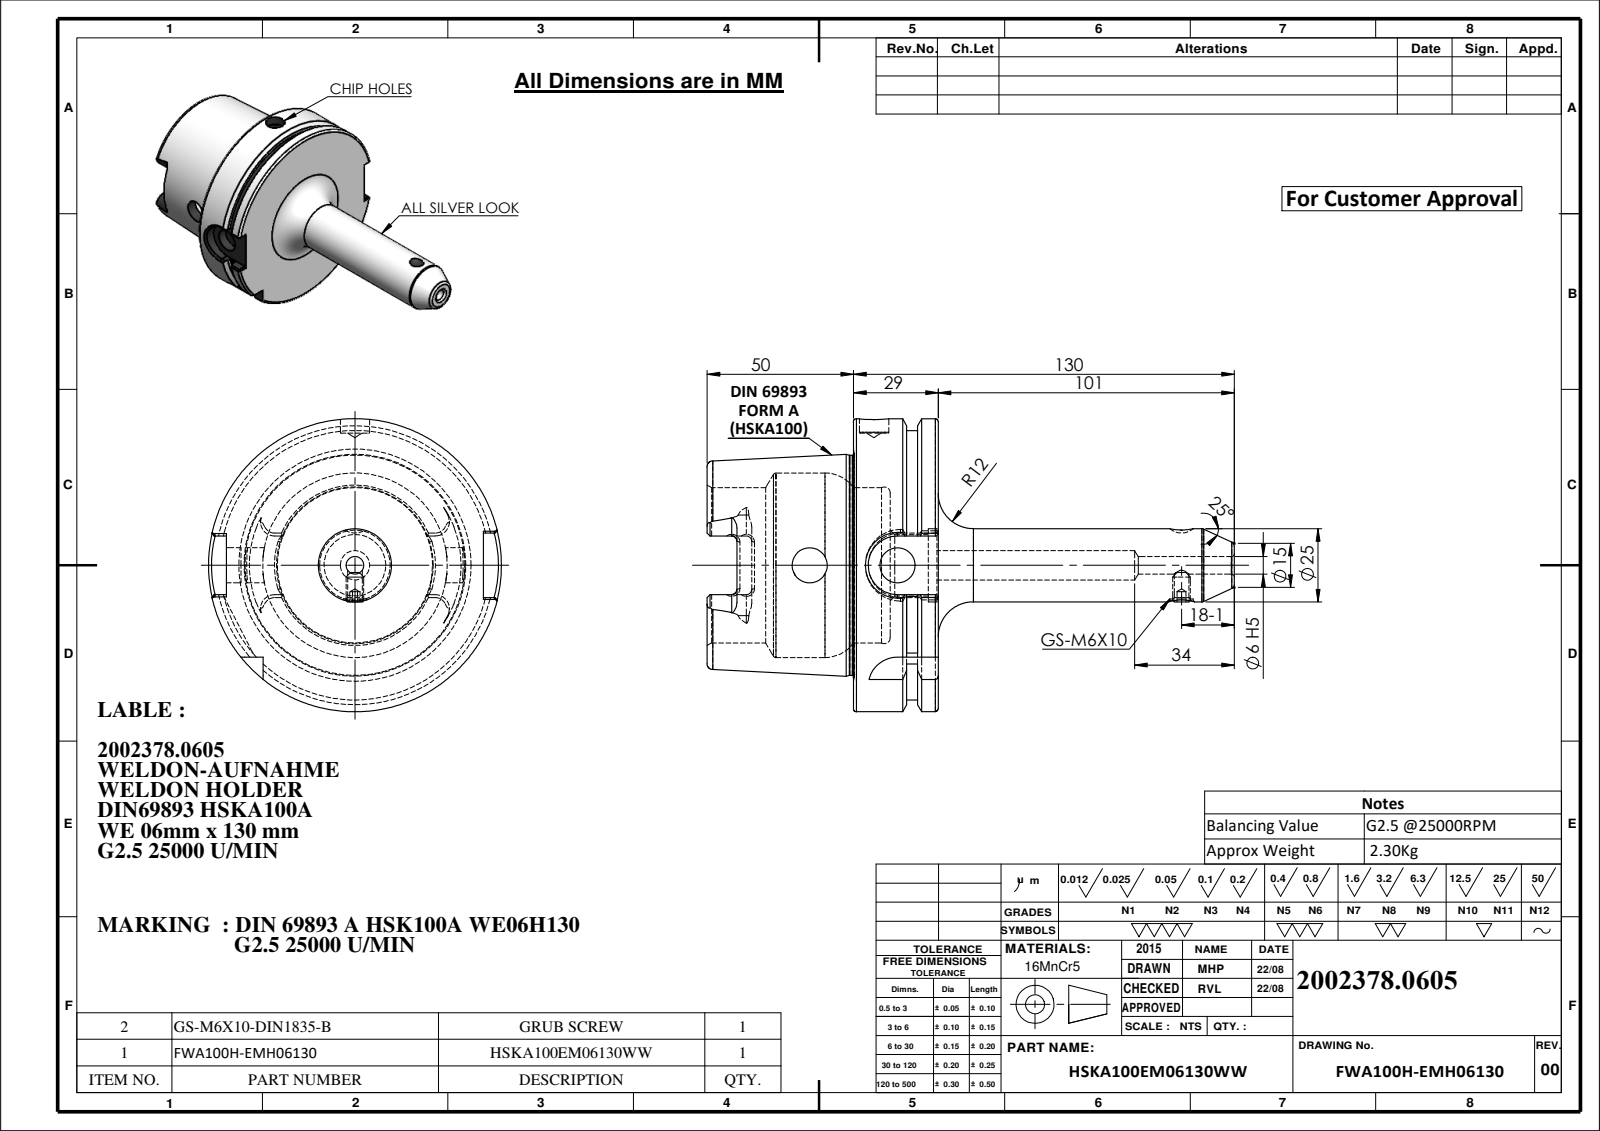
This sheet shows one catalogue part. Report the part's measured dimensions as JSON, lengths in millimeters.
{"part_name": "HSKA100EM06130WW; FWA100H-EMH06130; GS-M6X10-DIN1835-B", "step_written_by": "SolidWorks 2024 (CONFIG_CONTROL_DESIGN)", "units": "millimeters", "bodies": {"solids": 2, "faces": 208, "planar": 66, "cylindrical": 56, "other": 86}, "overall_size": [180, 100, 100], "volume_mm3": 298065, "surface_area_mm2": 60122, "round_holes": [[10, 2], [12, 2], [5, 1], [6, 1], [8, 1], [21, 1], [25, 1], [53, 1], [63, 1]], "round_bosses_or_shafts": [[100, 1], [92, 1], [75.16, 1], [6, 1]], "partial_cylinders_radius": [[1.8, 6], [4.88, 4], [10, 2], [11, 1]], "face_to_face_distances": [28.95, 12.5, 16.45, 50, 62.5, 78.95, 78.5, 28.5, 16, 0.45], "hole_center_spacings": [30, 105]}
